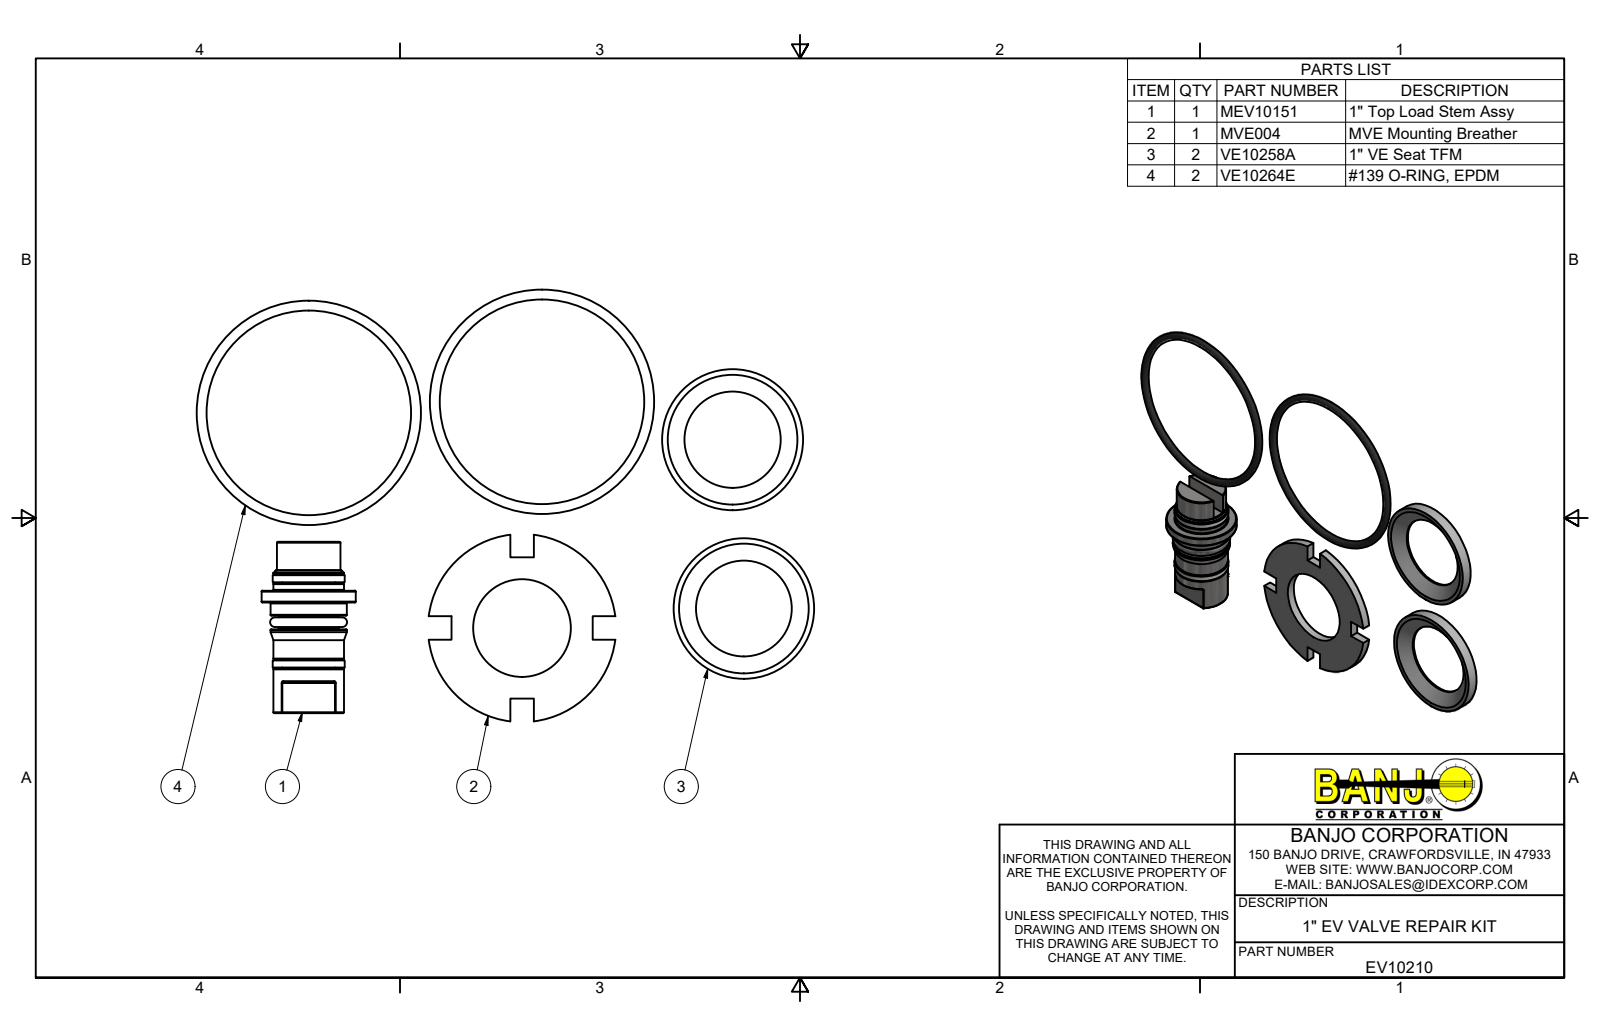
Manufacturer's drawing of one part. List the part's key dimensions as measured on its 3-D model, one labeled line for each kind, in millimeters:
Part name (STEP PRODUCT): EV10210; MEV10151; MEV10151SS; FP26041E (+5 more)
STEP written by: Autodesk Inventor 2019 (AUTOMOTIVE_DESIGN)
Units: millimetres
Bodies: 11 solids, 129 faces (44 planar, 33 cylindrical, 52 other)
Overall size (bounding box): 166.6 × 116.5 × 25.4
Volume: 22 090 mm³ · Surface area: 16 500 mm²
Round holes (diameter × count): ⌀25.9 ×2, ⌀16.4 ×1, ⌀26.4 ×1
Round bosses / shafts (diameter × count): ⌀38 ×2, ⌀50.8 ×1, ⌀25.4 ×1, ⌀20.6 ×1, ⌀19.4 ×1, ⌀19.1 ×1, ⌀17.8 ×1, ⌀16.2 ×1
Partial cylindrical surfaces — rounded edges, fillets, slot ends (radius × count): R0.3 ×8
Main face-to-face distances: 3, 1, 4, 23, 2.2, 3.8, 8.6, 33, 26.3, 7.6
Hole centre spacings: 45.6, 60.1, 76.3
